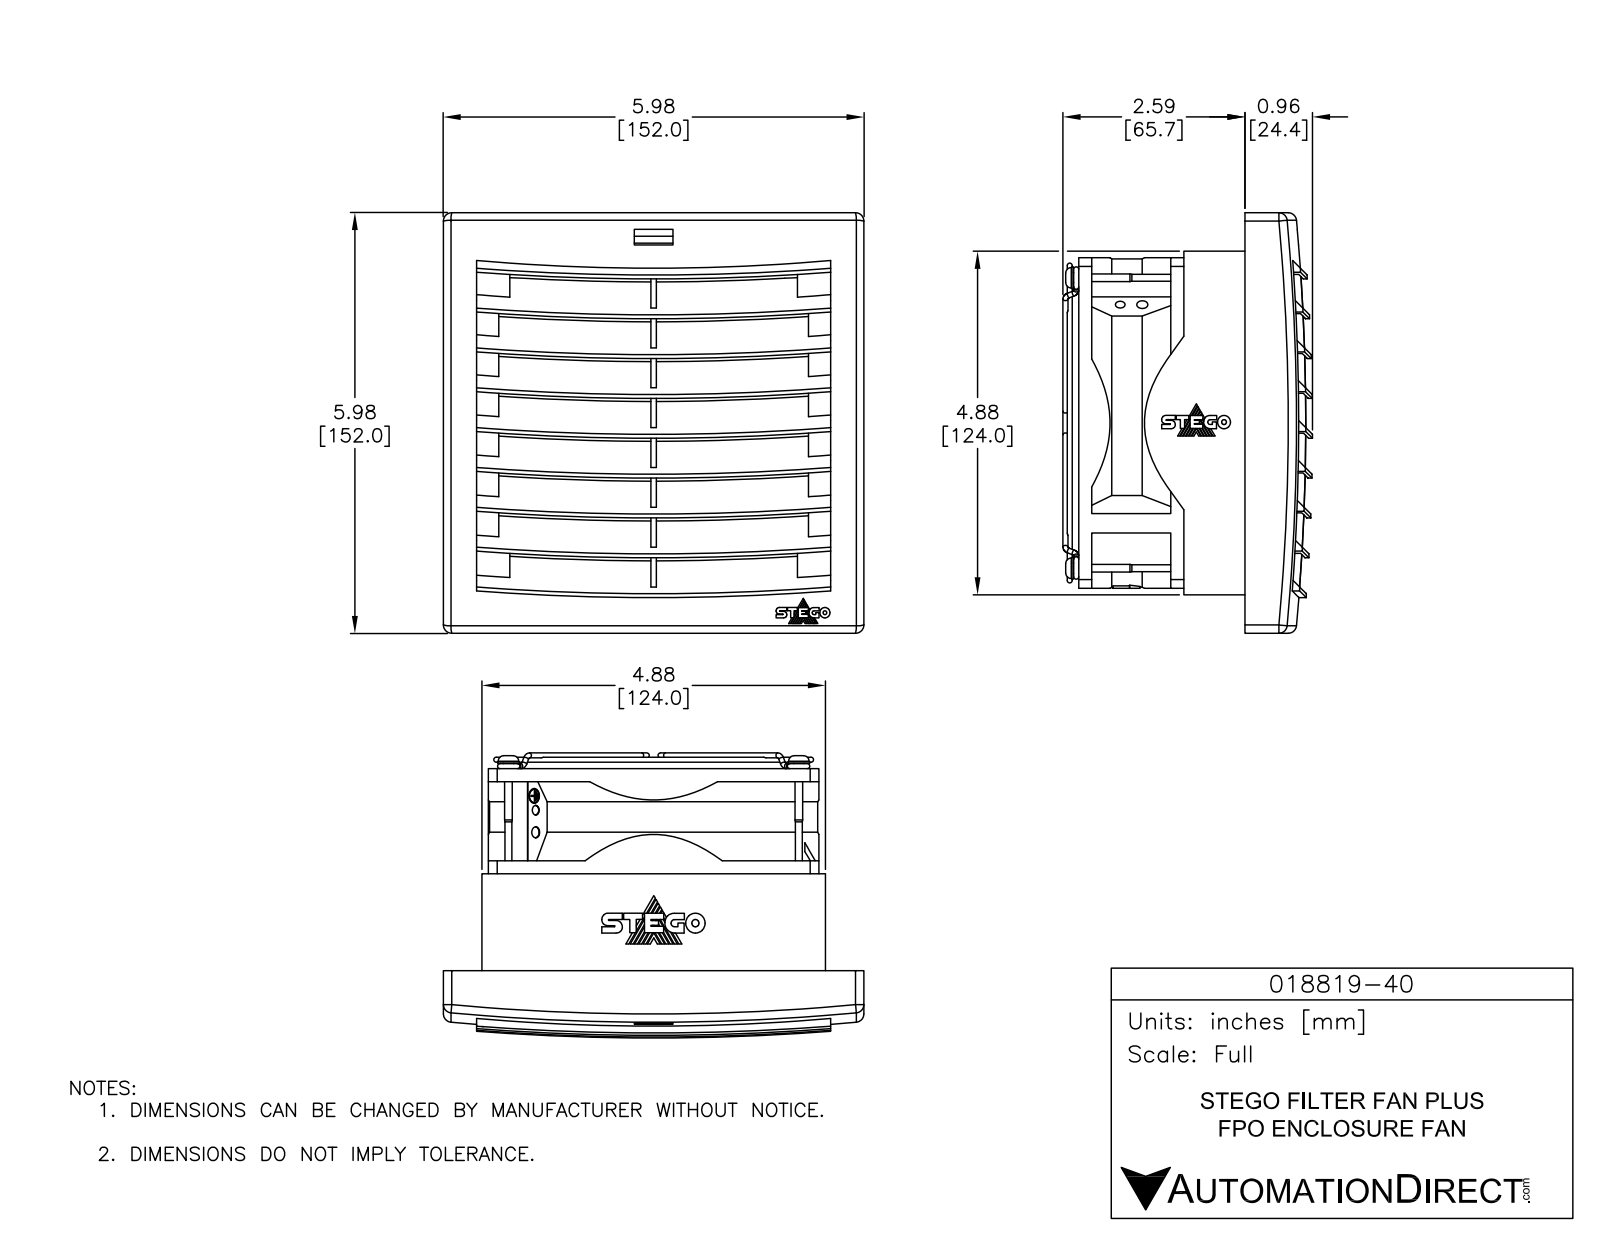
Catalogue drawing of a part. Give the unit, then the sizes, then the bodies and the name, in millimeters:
Units: millimetres
Overall size (bounding box): 152 × 152 × 104
Round holes (diameter × count): ⌀6.5 ×4, ⌀24.9 ×1, ⌀42.2 ×1, ⌀59.4 ×1, ⌀76.7 ×1, ⌀82.6 ×1, ⌀96 ×1, ⌀105.4 ×1
Round bosses / shafts (diameter × count): ⌀110.4 ×1, ⌀88.6 ×1, ⌀80.7 ×1, ⌀68.9 ×1, ⌀63.4 ×1, ⌀46.2 ×1, ⌀33.6 ×1, ⌀28.9 ×1
Partial cylindrical surfaces — rounded edges, fillets, slot ends (radius × count): R349.4 ×16, R47 ×5, R3 ×4, R3.6 ×4, R13.2 ×1, R21.6 ×1, R24.6 ×1, R31.4 ×1
Main face-to-face distances: 10.8, 1.5, 3.1, 120.9, 21.6, 2, 12.3, 9.3, 117.8, 14
Hole centre spacings: 76.4, 108, 152.7
Volume: 516 200 mm³ · Surface area: 202 800 mm²
Bodies: 1 solid, 520 faces (305 planar, 207 cylindrical, 8 other)
Part name (STEP PRODUCT): 018819-40
STEP written by: SolidWorks 2018 (AUTOMOTIVE_DESIGN)
